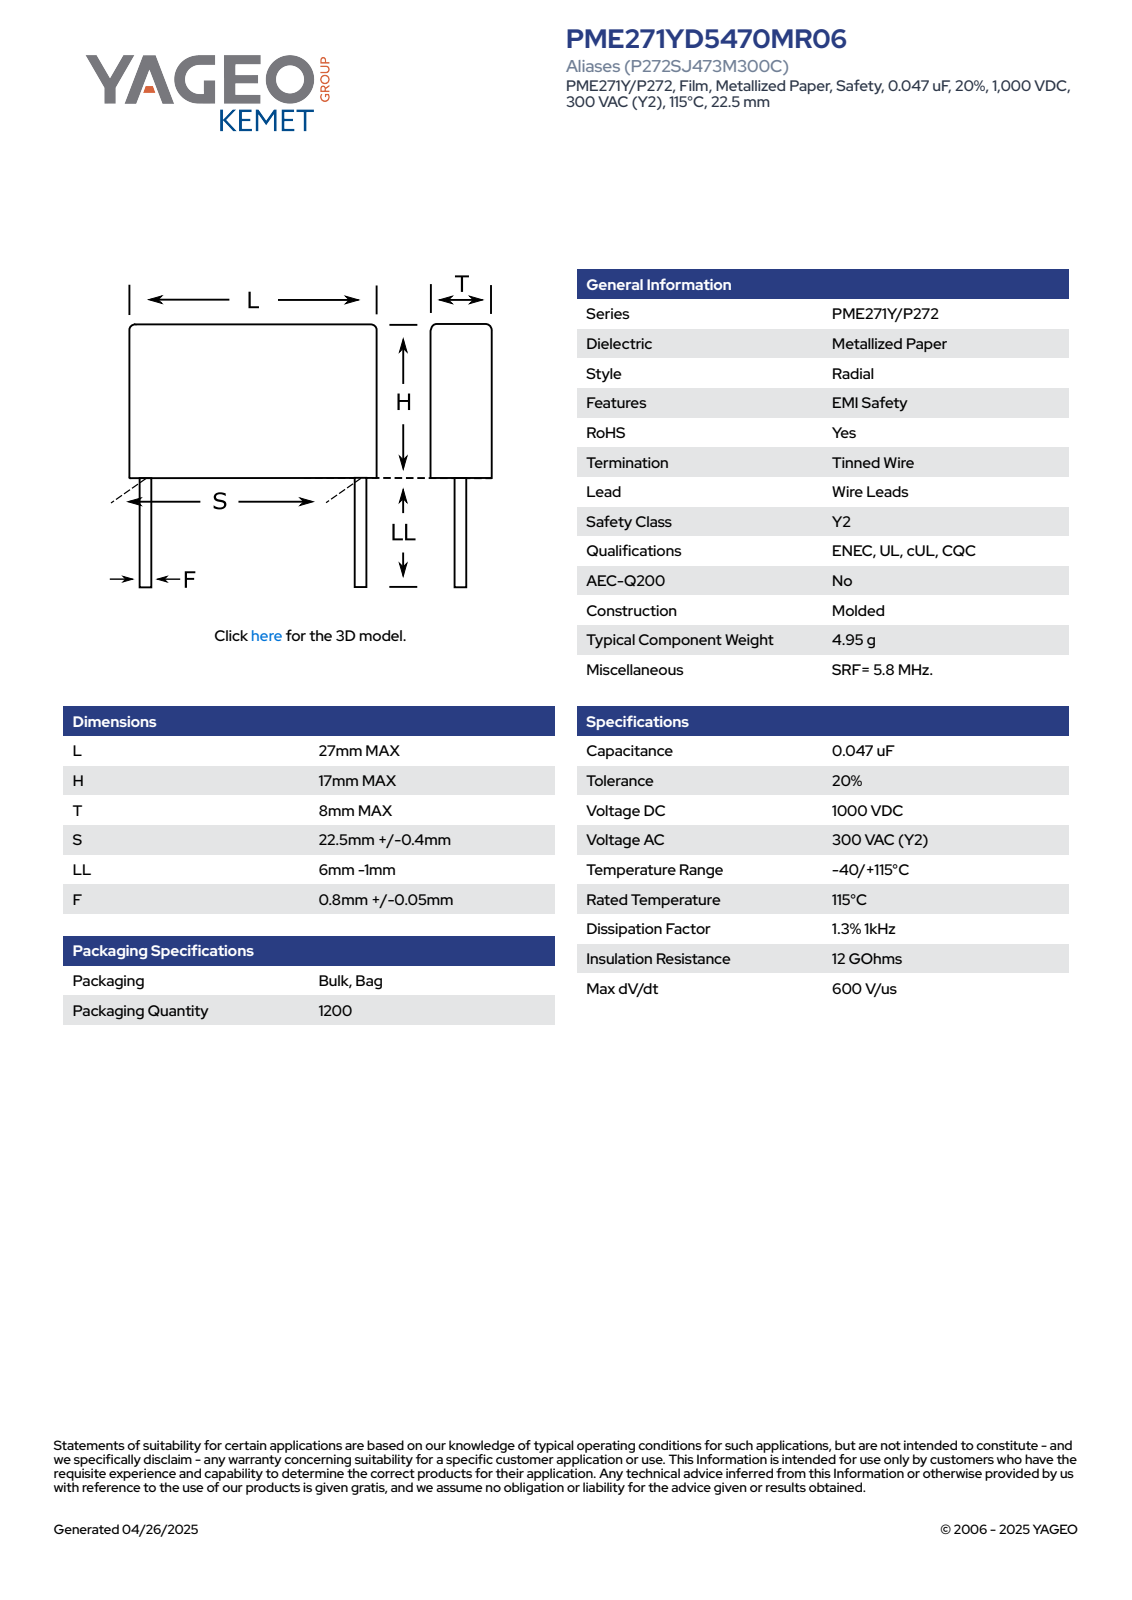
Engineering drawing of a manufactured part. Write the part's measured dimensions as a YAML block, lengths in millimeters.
part_name: "CFR_MOLDED_27X17X8_L27H17T8S22.5LL5F0.85"
step_written_by: "SolidWorks 2014 (AUTOMOTIVE_DESIGN)"
units: millimeters
bodies: {solids: 4, faces: 73, planar: 65, cylindrical: 8, other: 0}
overall_size: [27, 22, 8.01]
volume: 3674
surface_area: 1669
round_bosses_or_shafts:
  - {diameter: 0.85, count: 2}
partial_cylinders:
  - {radius: 0.5, count: 4}
face_to_face_distances: [8, 17, 27, 8.01, 5, 22, 14.55, 9.55, 7.45, 12.13]
